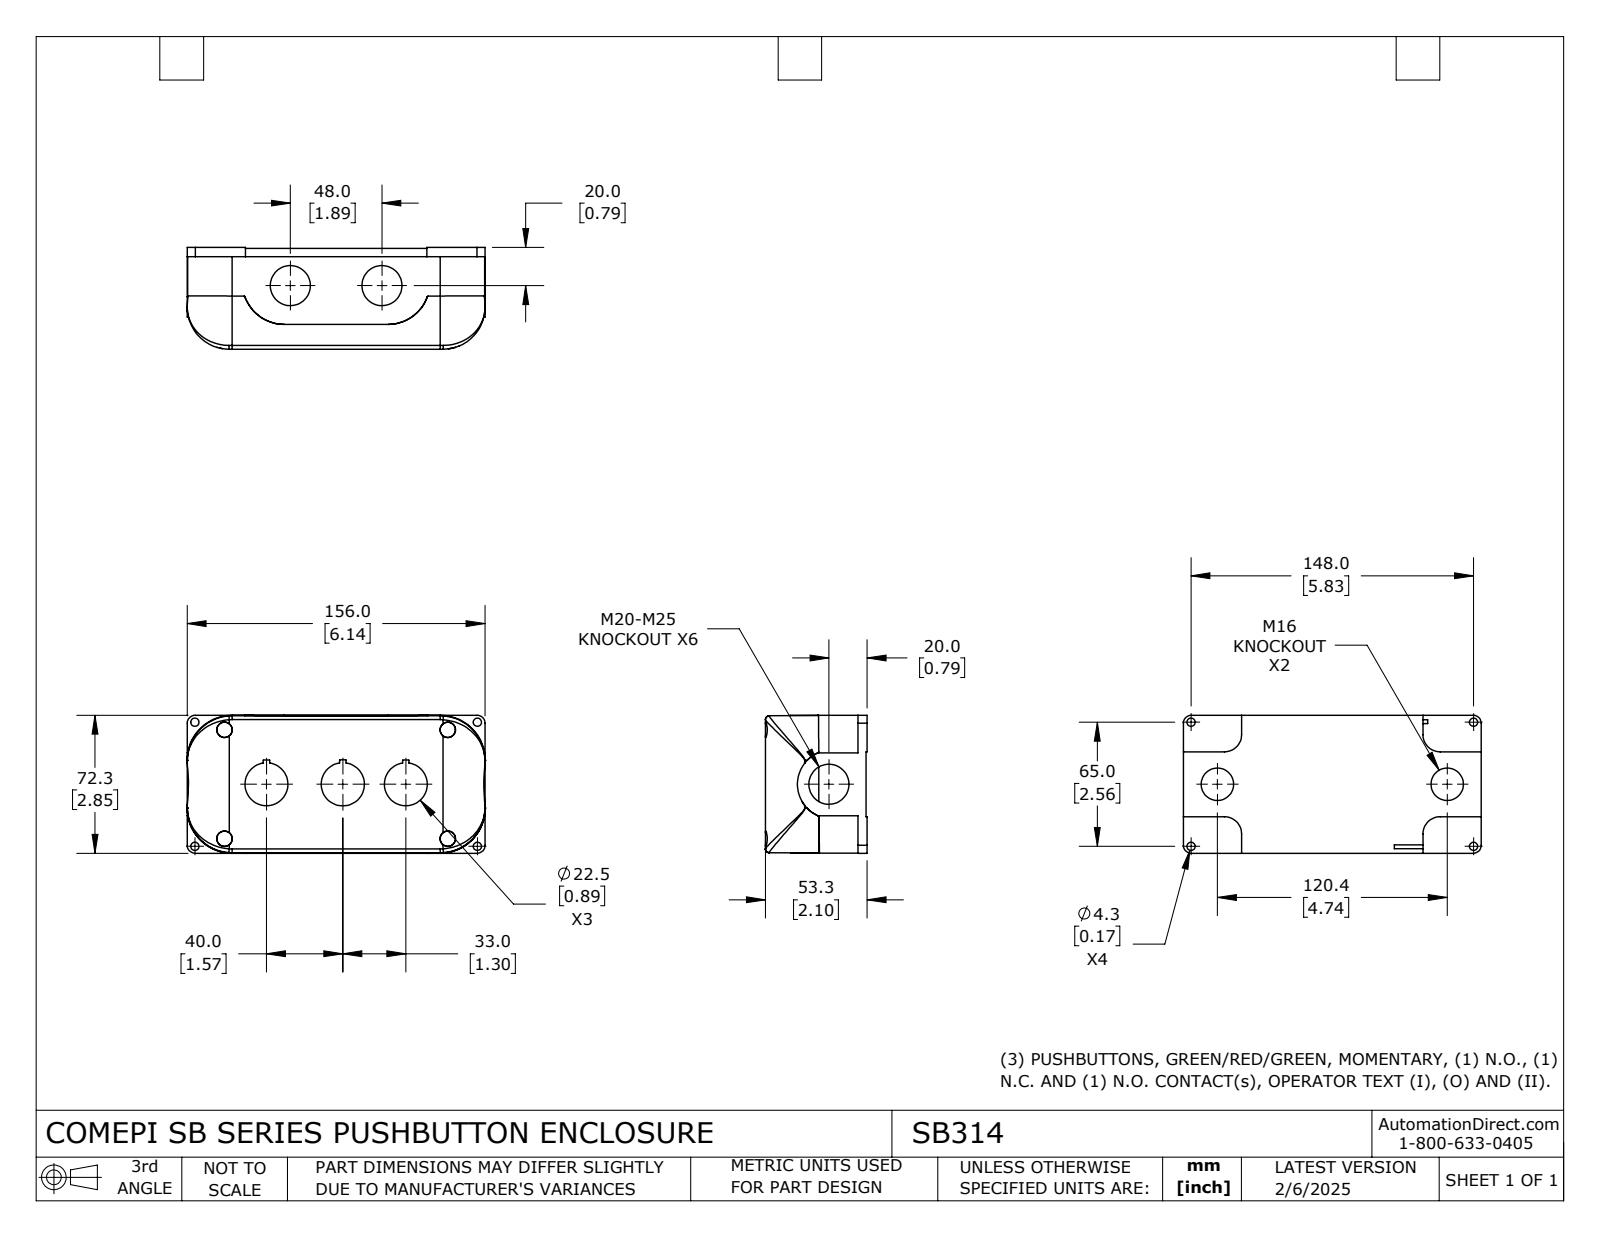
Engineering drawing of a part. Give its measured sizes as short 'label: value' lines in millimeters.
name: SB314
written by: SolidWorks 2024 (CONFIG_CONTROL_DESIGN)
unit: mm
bodies: 2 solids, 332 faces (162 planar, 82 cylindrical, 88 other)
size: 156 × 72.3 × 53.3
volume: 302 200 mm³; area: 84 640 mm²
holes: 4× ⌀4.3, 3× ⌀21, 2× ⌀17, 1× ⌀22.6
rounds: 4× R0.9, 4× R2, 4× R4, 4× R9, 4× R9.7, 4× R22, 4× R23.6, 2× R20
face distances: 2.5, 52.8, 50.3, 39.8, 37.3, 13, 28, 15, 24.8, 22.3
hole spacings: 35.3, 138.1, 65, 77.6, 84, 148, 161.6, 48
